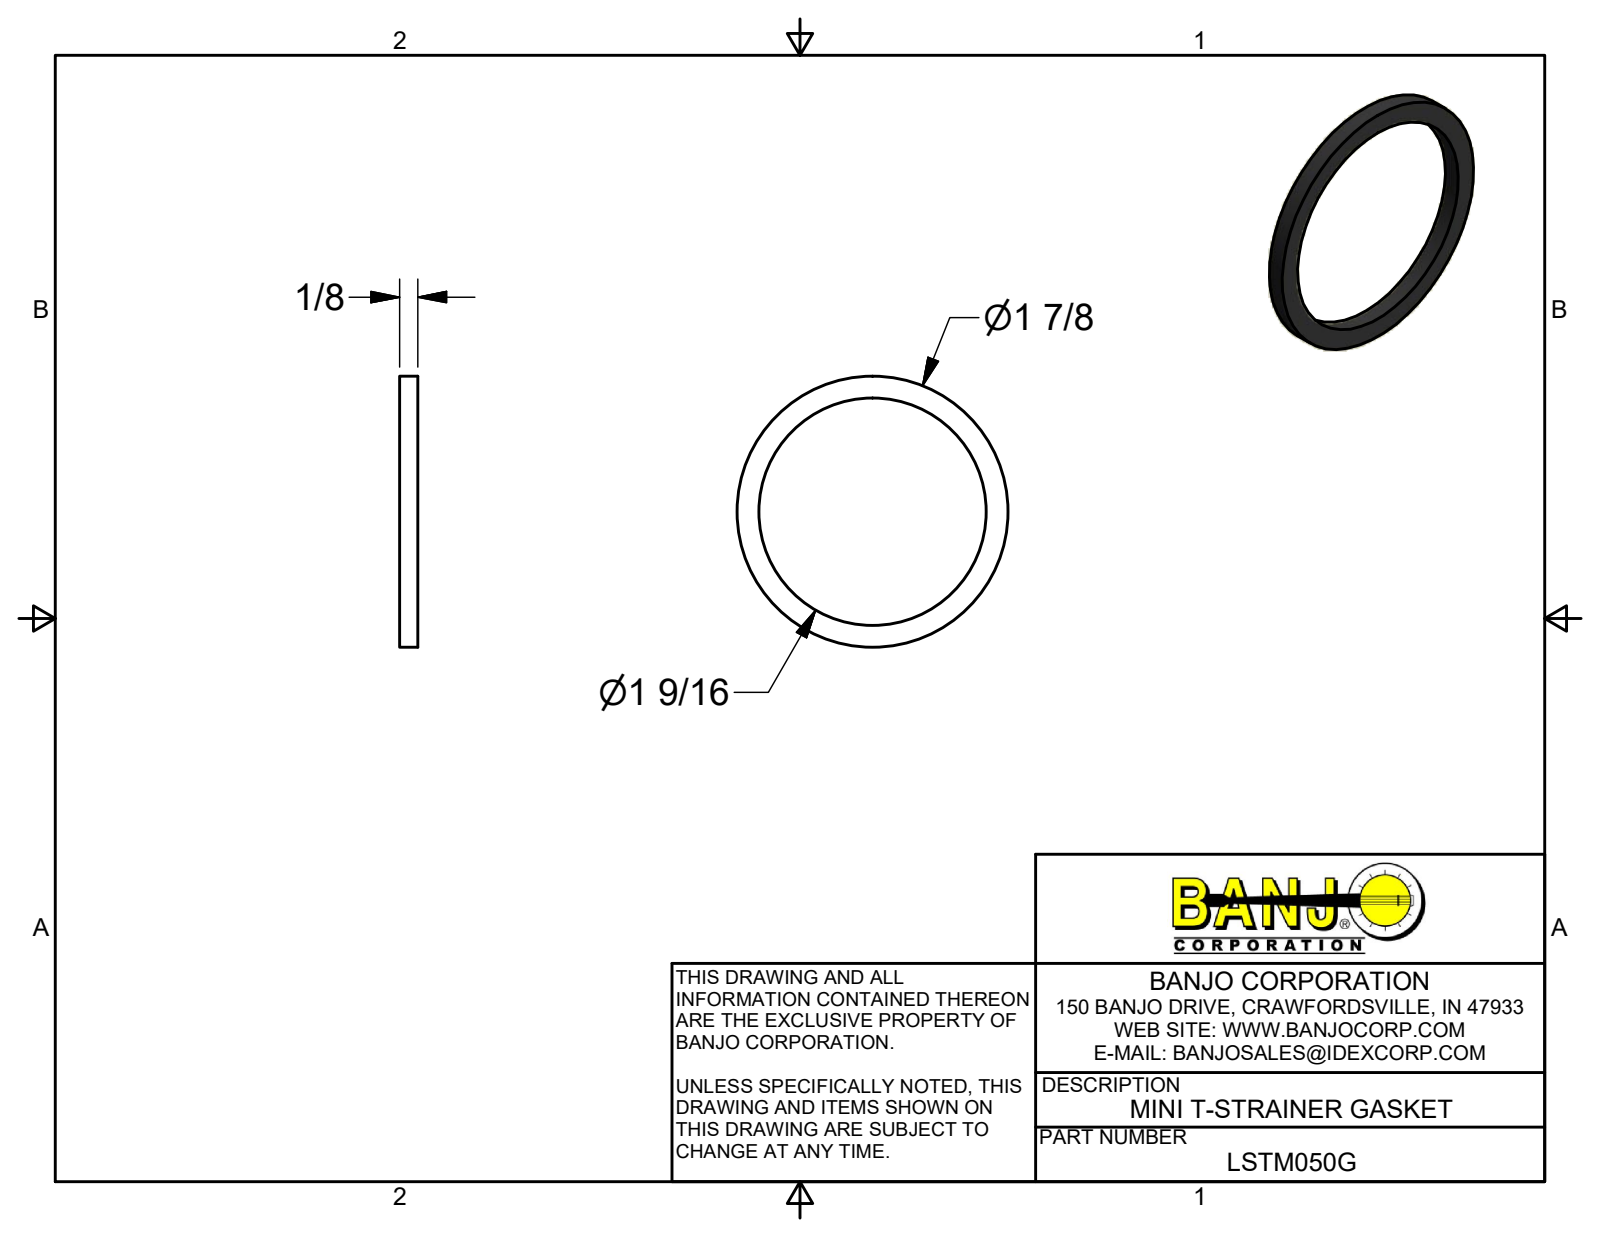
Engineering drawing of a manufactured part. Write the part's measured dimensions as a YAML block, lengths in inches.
part_name: "LSTM050G"
step_written_by: "Autodesk Inventor 2017 (AUTOMOTIVE_DESIGN)"
units: inches
bodies: {solids: 1, faces: 4, planar: 2, cylindrical: 2, other: 0}
overall_size: [1.861, 1.861, 0.125]
volume: 0.1
surface_area: 2.948
round_holes:
  - {diameter: 1.563, count: 1}
round_bosses_or_shafts:
  - {diameter: 1.861, count: 1}
face_to_face_distances: [0.125]
